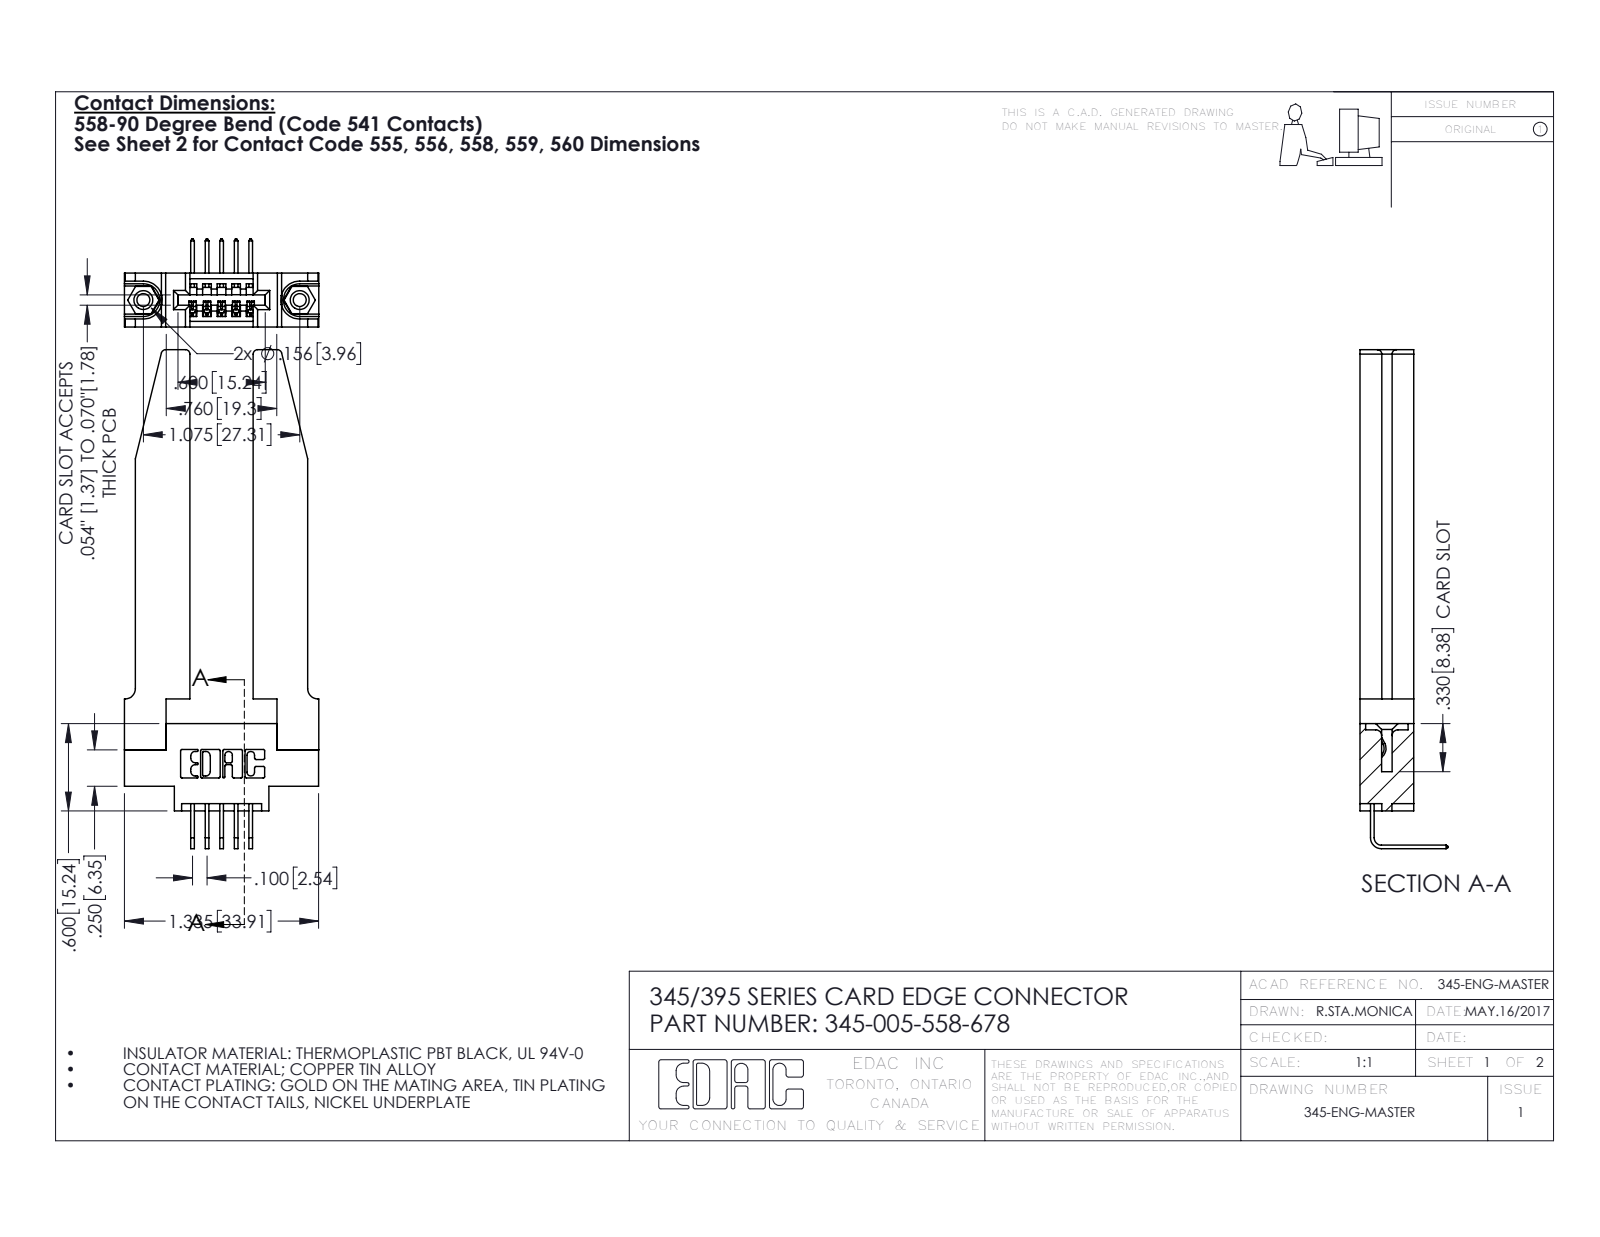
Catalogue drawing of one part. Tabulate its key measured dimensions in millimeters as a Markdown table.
| quantity | value |
| --- | --- |
| part name | 345-220-078_345-220-078; 345-250-001_345-250-001-102; 345-292-001_558 Tail - 2; 345 Part_0.170 Offset - 0.156 Dia-TH (+1 more) |
| STEP written by | SolidWorks 2016 (CONFIG_CONTROL_DESIGN) |
| units | millimeters |
| bodies | 10 solids, 664 faces (436 planar, 176 cylindrical, 52 other) |
| overall size | 87.1 × 33.9 × 15.4 |
| volume | 10 600 mm³ |
| surface area | 10 320 mm² |
| round holes (diameter × count) | 2.3 × 2, 3.2 × 2, 4 × 2, 1.6 × 1 |
| round bosses / shafts (diameter × count) | 3.9 × 2 |
| partial cylindrical surfaces (radius × count) | 0.3 × 22, 0.2 × 10, 0.8 × 8, 0.2 × 6, 0.8 × 6, 0.7 × 3, 0.8 × 2, 1 × 2 |
| main face-to-face distances | 9.4, 3.8, 5.6, 11, 1.8, 3.8, 7.6, 2, 2.4, 1.8 |
| hole center spacings | 6.9, 21.5, 27.3 |
